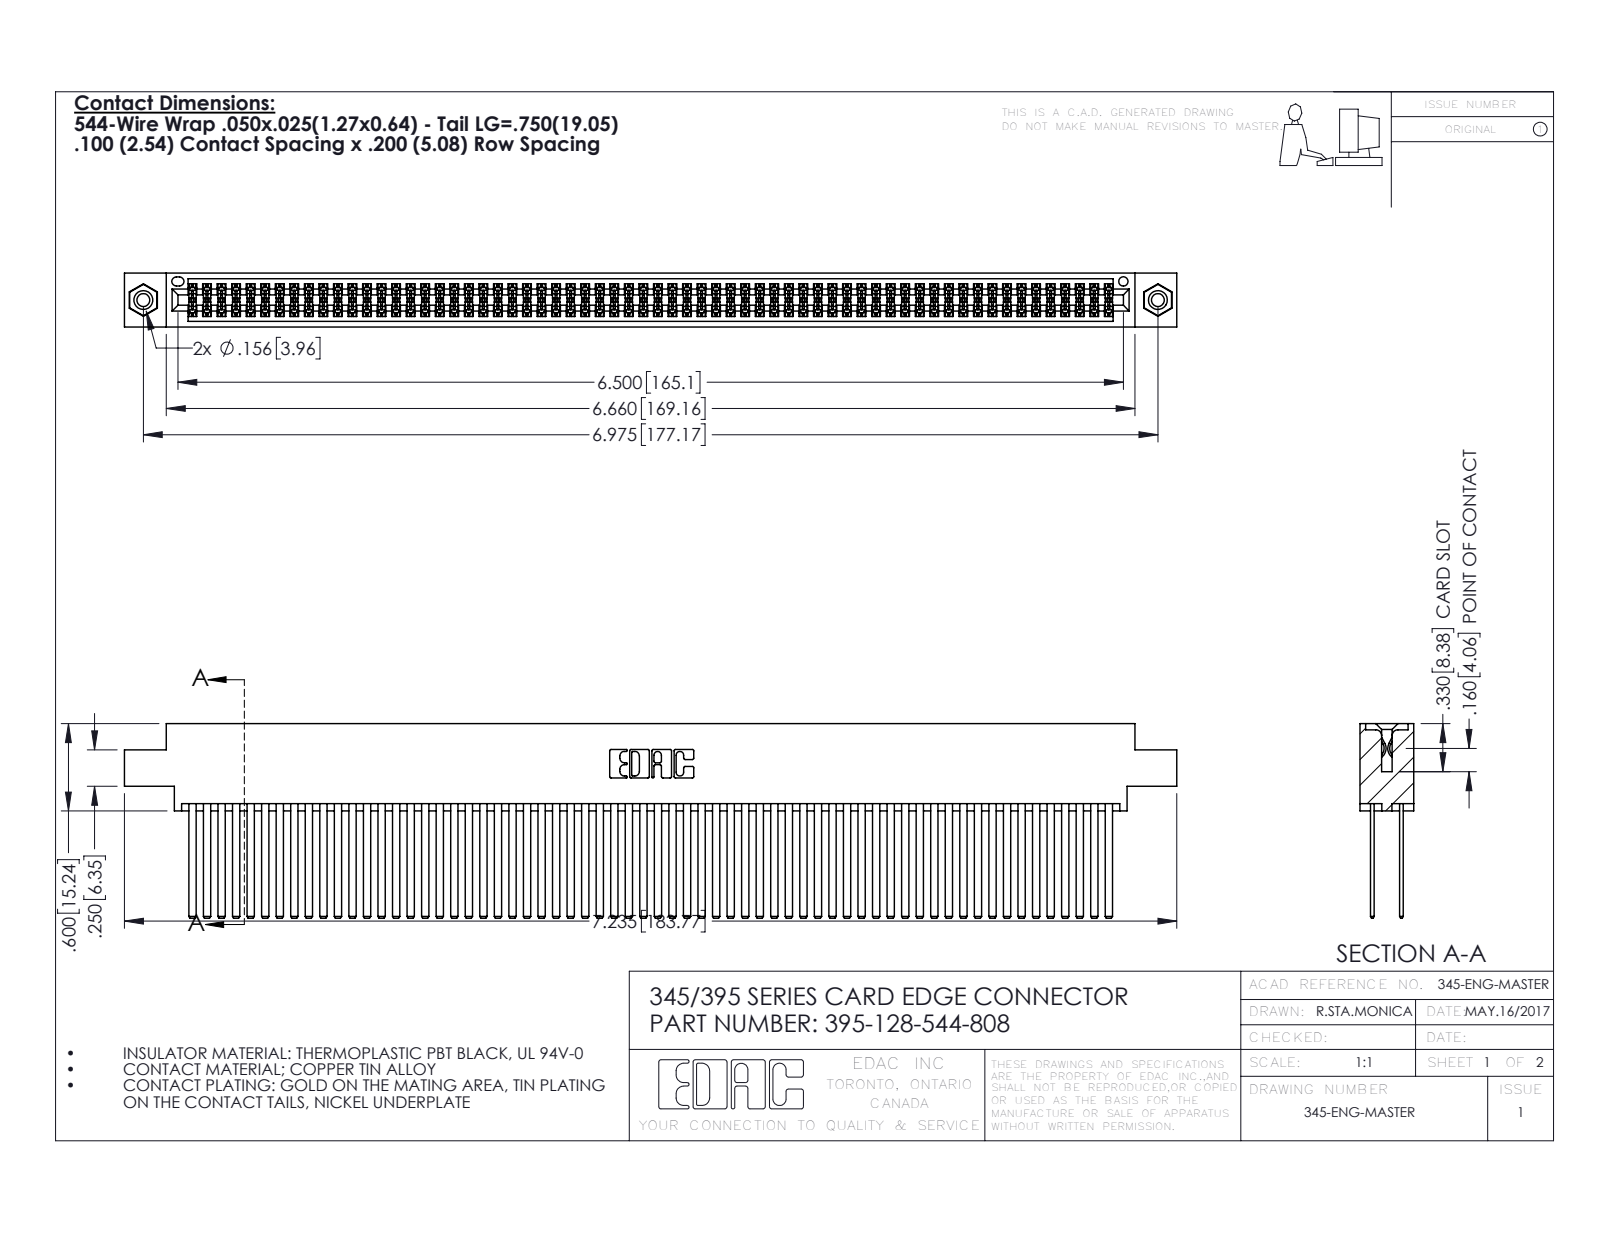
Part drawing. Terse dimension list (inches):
name: 345-250-001_345-250-003-102; 395-128-544-808; 345-292-001_345-293-144; 345 Part_0.170 Offset - 0.156 Dia-TI
written by: SolidWorks 2016 (CONFIG_CONTROL_DESIGN)
unit: in
bodies: 131 solids, 5822 faces (3828 planar, 1978 cylindrical, 16 other)
size: 7.235 × 1.337 × 0.37
volume: 1.204 in³; area: 54.26 in²
holes: 2× ⌀0.089, 2× ⌀0.125, 2× ⌀0.156, 1× ⌀0.064
bosses: 2× ⌀0.155
rounds: 192× R0.006, 22× R0.01, 6× R0.007, 6× R0.031, 3× R0.026, 2× R0.014, 2× R0.019, 2× R0.022
face distances: 0.2, 0.025, 0.072, 0.098, 0.272, 0.298, 0.225, 0.175, 0.37, 0.15
hole spacings: 0.27, 6.739, 6.975
